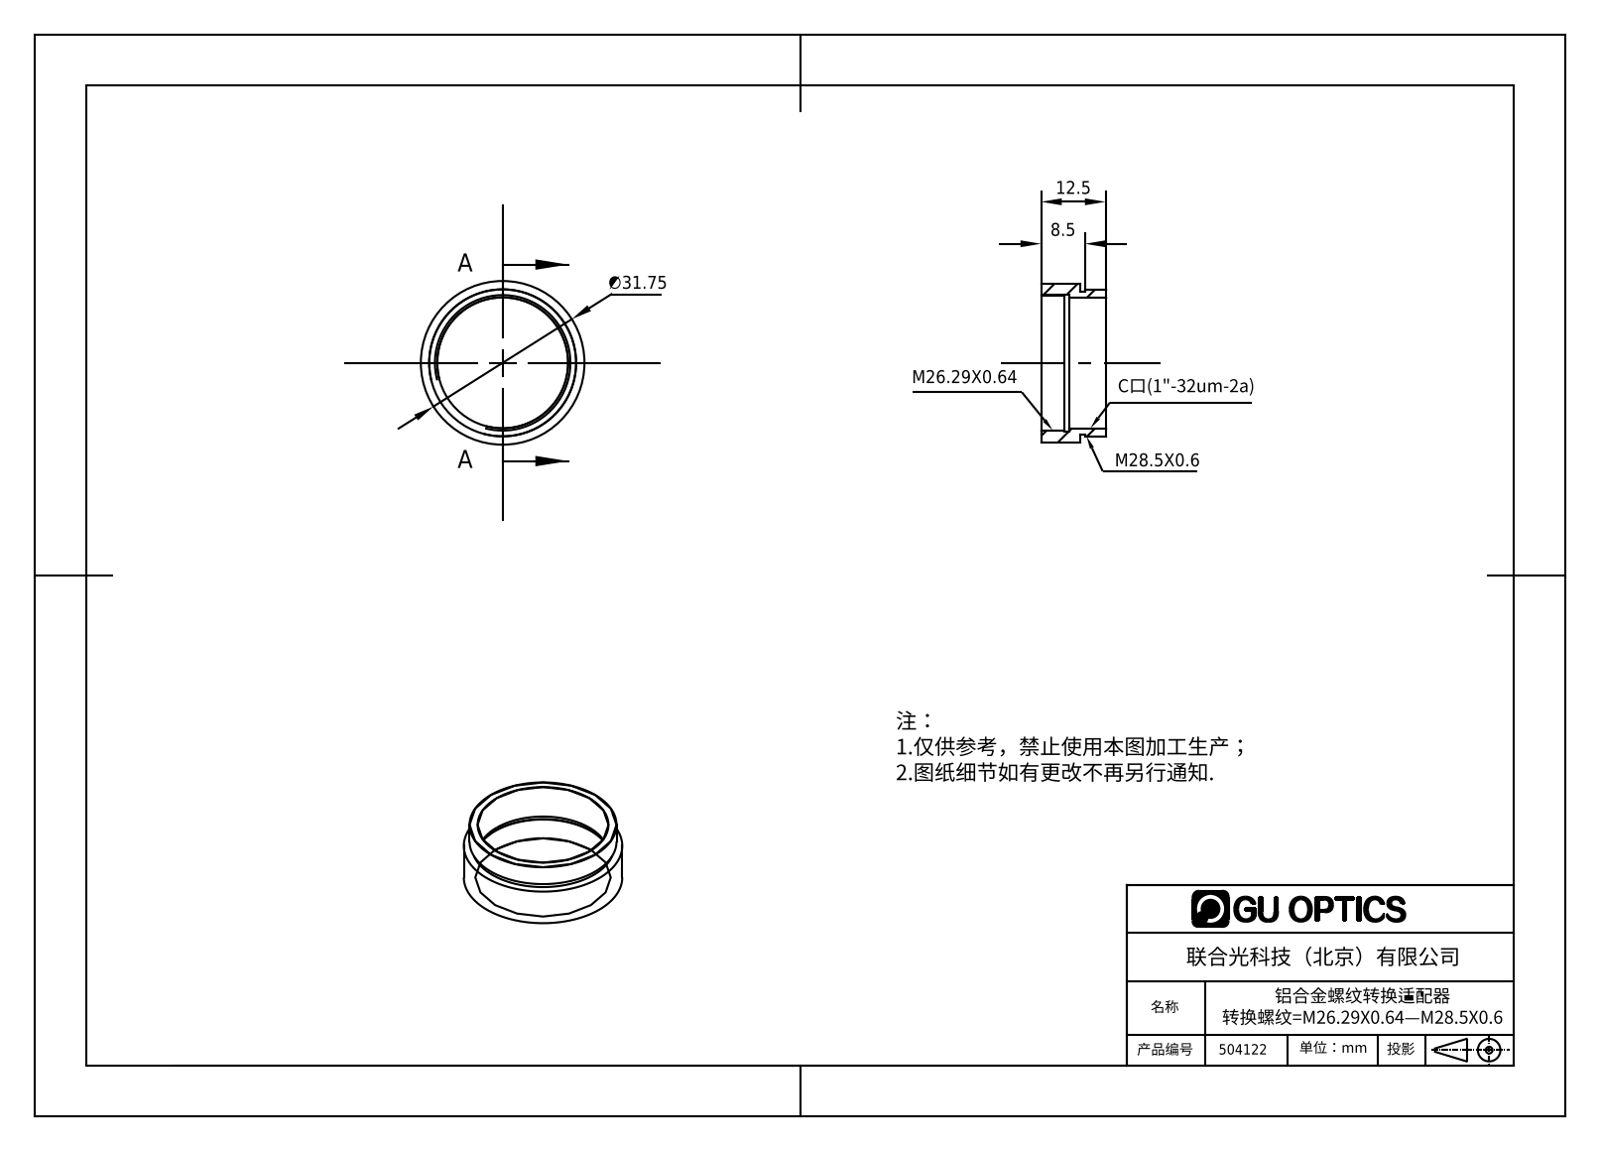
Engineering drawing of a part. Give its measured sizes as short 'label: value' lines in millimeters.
name: 504122
written by: SolidWorks 2016 (AUTOMOTIVE_DESIGN)
unit: mm
bodies: 1 solid, 18 faces (6 planar, 12 cylindrical, 0 other)
size: 31.75 × 31.75 × 12.5
volume: 2 577 mm³; area: 2 874 mm²
holes: 1× ⌀25.38, 1× ⌀26.2, 1× ⌀26.5
bosses: 1× ⌀31.75, 1× ⌀28.52, 1× ⌀27.7
face distances: 7.5, 12.5, 5, 1, 3, 4, 5.5, 2, 7, 8.5
